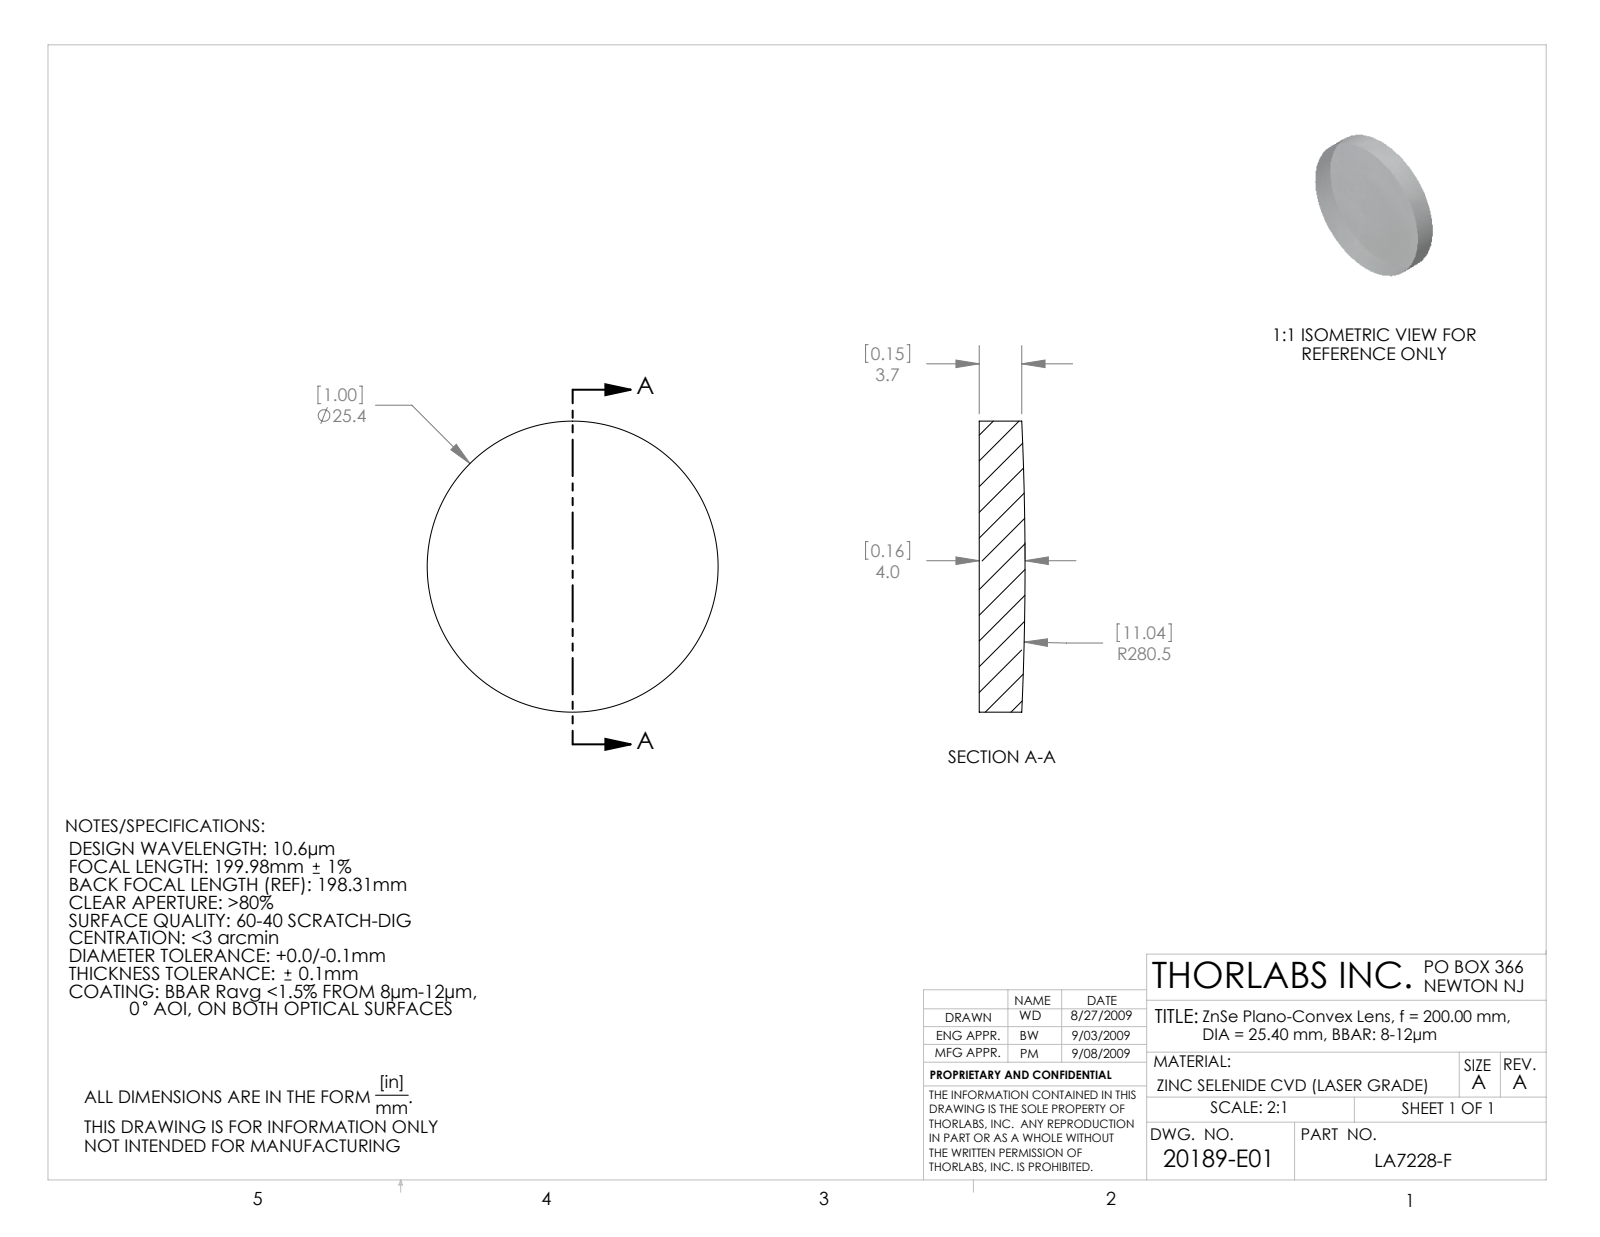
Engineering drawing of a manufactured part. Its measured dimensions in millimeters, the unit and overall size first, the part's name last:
Units: millimetres
Overall size (bounding box): 25.4 × 25.4 × 4
Round bosses / shafts (diameter × count): ⌀25.4 ×1
Volume: 1 954 mm³ · Surface area: 1 310 mm²
Bodies: 1 solid, 5 faces (1 planar, 2 cylindrical, 2 other)
Part name (STEP PRODUCT): 20189-E0W
STEP written by: SolidWorks 2007 (CONFIG_CONTROL_DESIGN)
